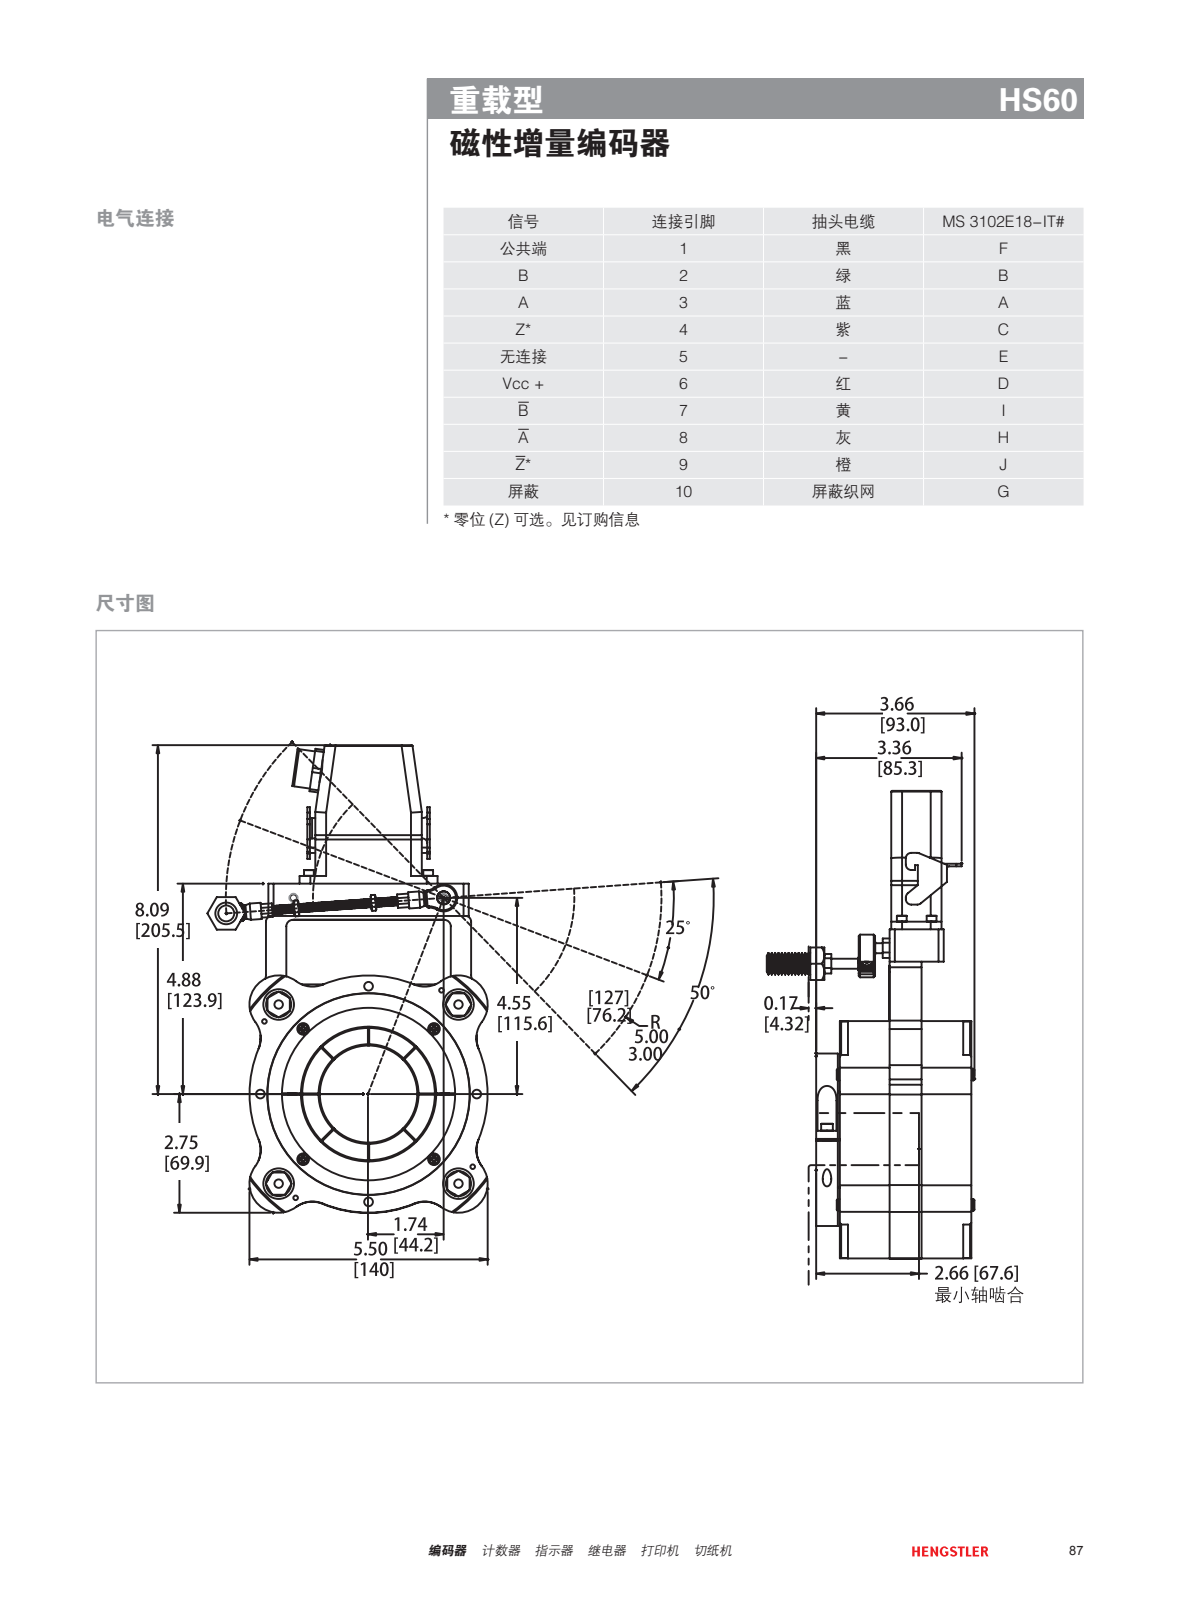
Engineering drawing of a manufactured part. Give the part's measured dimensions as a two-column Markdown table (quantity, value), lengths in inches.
| quantity | value |
| --- | --- |
| part name | HS60 |
| STEP written by | PRO/ENGINEER BY PARAMETRIC TECHNOLOGY CORPORATION, 2007030 (CONFIG_CONTROL_DESIGN) |
| units | inches |
| bodies | 2 solids, 616 faces (321 planar, 213 cylindrical, 82 other) |
| overall size | 11.387 × 5.504 × 3.838 |
| volume | 85.53 in³ |
| surface area | 313.4 in² |
| round holes (diameter × count) | 0.125 × 8, 0.107 × 4, 0.254 × 4, 0.426 × 4, 0.63 × 4, 0.136 × 2, 0.177 × 2, 0.26 × 2, 0.738 × 1, 3 × 1, 3.161 × 1, 3.228 × 1 |
| round bosses / shafts (diameter × count) | 4 × 1, 3.15 × 1, 0.87 × 1 |
| partial cylindrical surfaces (radius × count) | 0.197 × 8, 0.25 × 6, 0.596 × 6, 0.118 × 5, 0.039 × 4, 0.079 × 4, 0.12 × 4, 0.236 × 4 |
| main face-to-face distances | 1.25, 3.238, 1.988, 0.738, 0.5, 1.8, 1.322, 0.072, 0.667, 1.917 |
| hole center spacings | 4.154, 0.512, 1.688, 2.12, 2.541, 2.938, 3.776, 4.5 |
